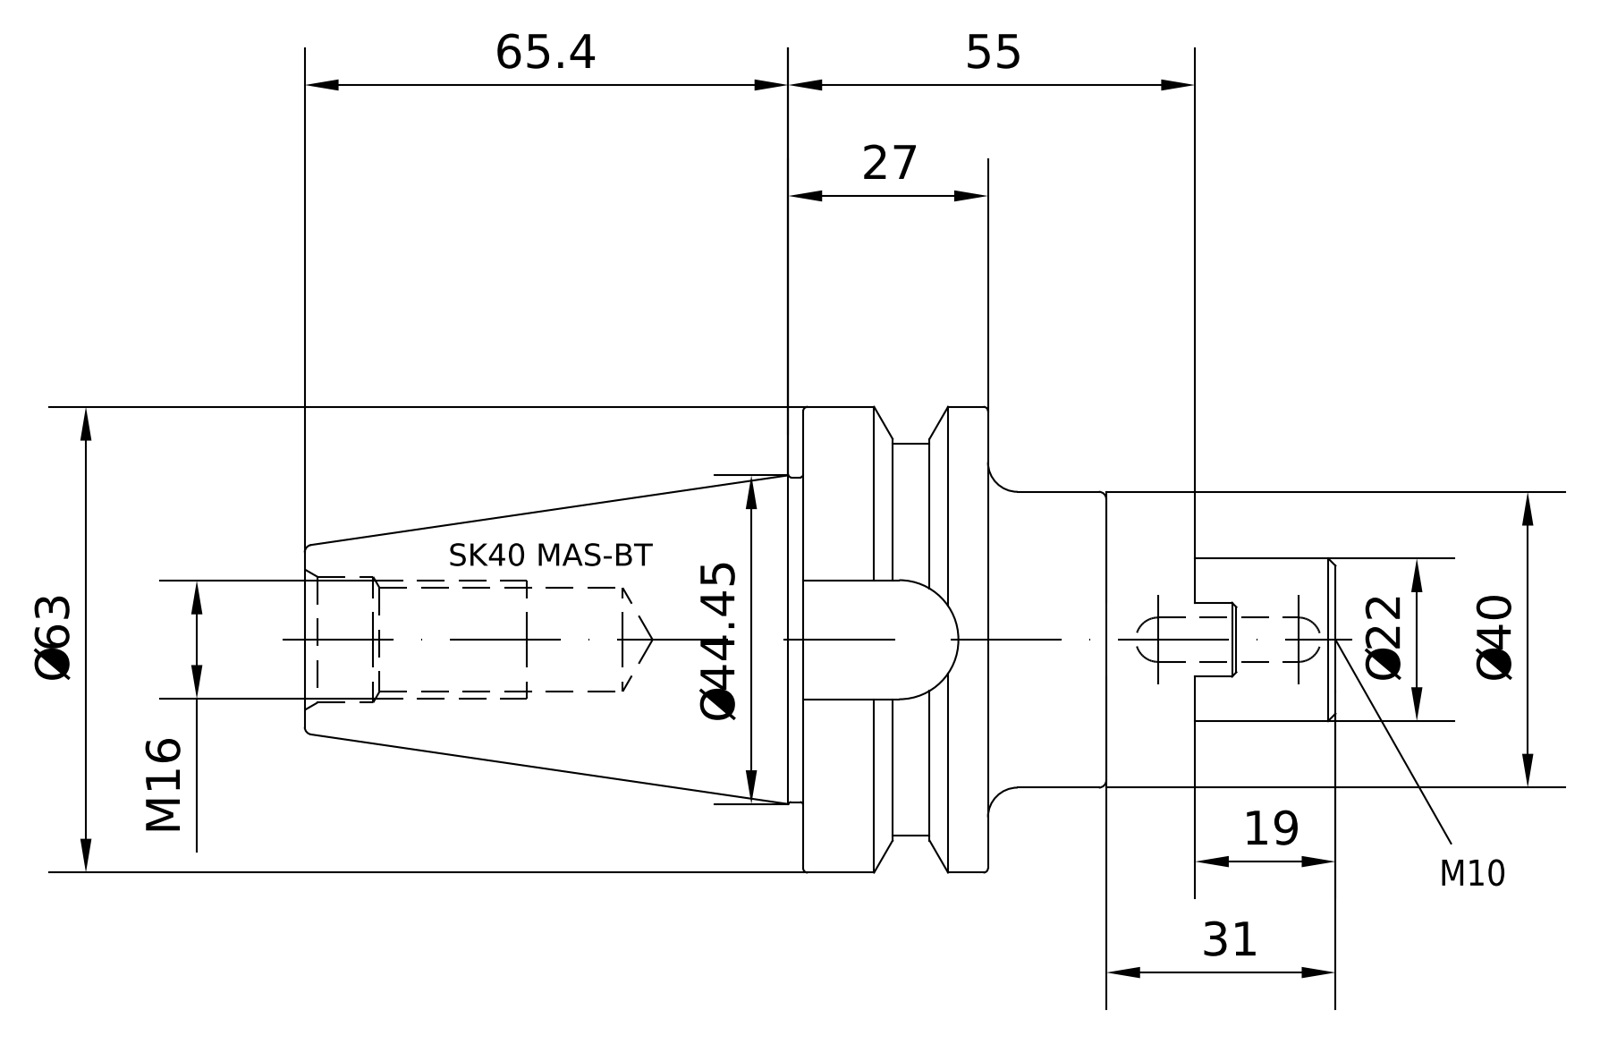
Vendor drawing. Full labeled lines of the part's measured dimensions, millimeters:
Part name (STEP PRODUCT): 40-540-22; 85-200-22; 40-540-22_ASM
STEP written by: PRO/ENGINEER BY PARAMETRIC TECHNOLOGY CORPORATION, 2010430 (CONFIG_CONTROL_DESIGN)
Units: millimetres
Bodies: 2 solids, 188 faces (92 planar, 38 cylindrical, 58 other)
Overall size (bounding box): 139.4 × 62.98 × 62.98
Volume: 165 042 mm³ · Surface area: 32 921 mm²
Round holes (diameter × count): ⌀8.5 ×1, ⌀10 ×1, ⌀13.84 ×1, ⌀17.01 ×1, ⌀17.5 ×1, ⌀22.36 ×1, ⌀26 ×1
Round bosses / shafts (diameter × count): ⌀62.98 ×1, ⌀52.75 ×1, ⌀43.75 ×1, ⌀40 ×1, ⌀22 ×1, ⌀16.01 ×1
Partial cylindrical surfaces — rounded edges, fillets, slot ends (radius × count): R3 ×2, R5.05 ×1, R8.1 ×1
Main face-to-face distances: 16, 25, 41, 53, 28, 12, 44.9, 1, 11, 72
